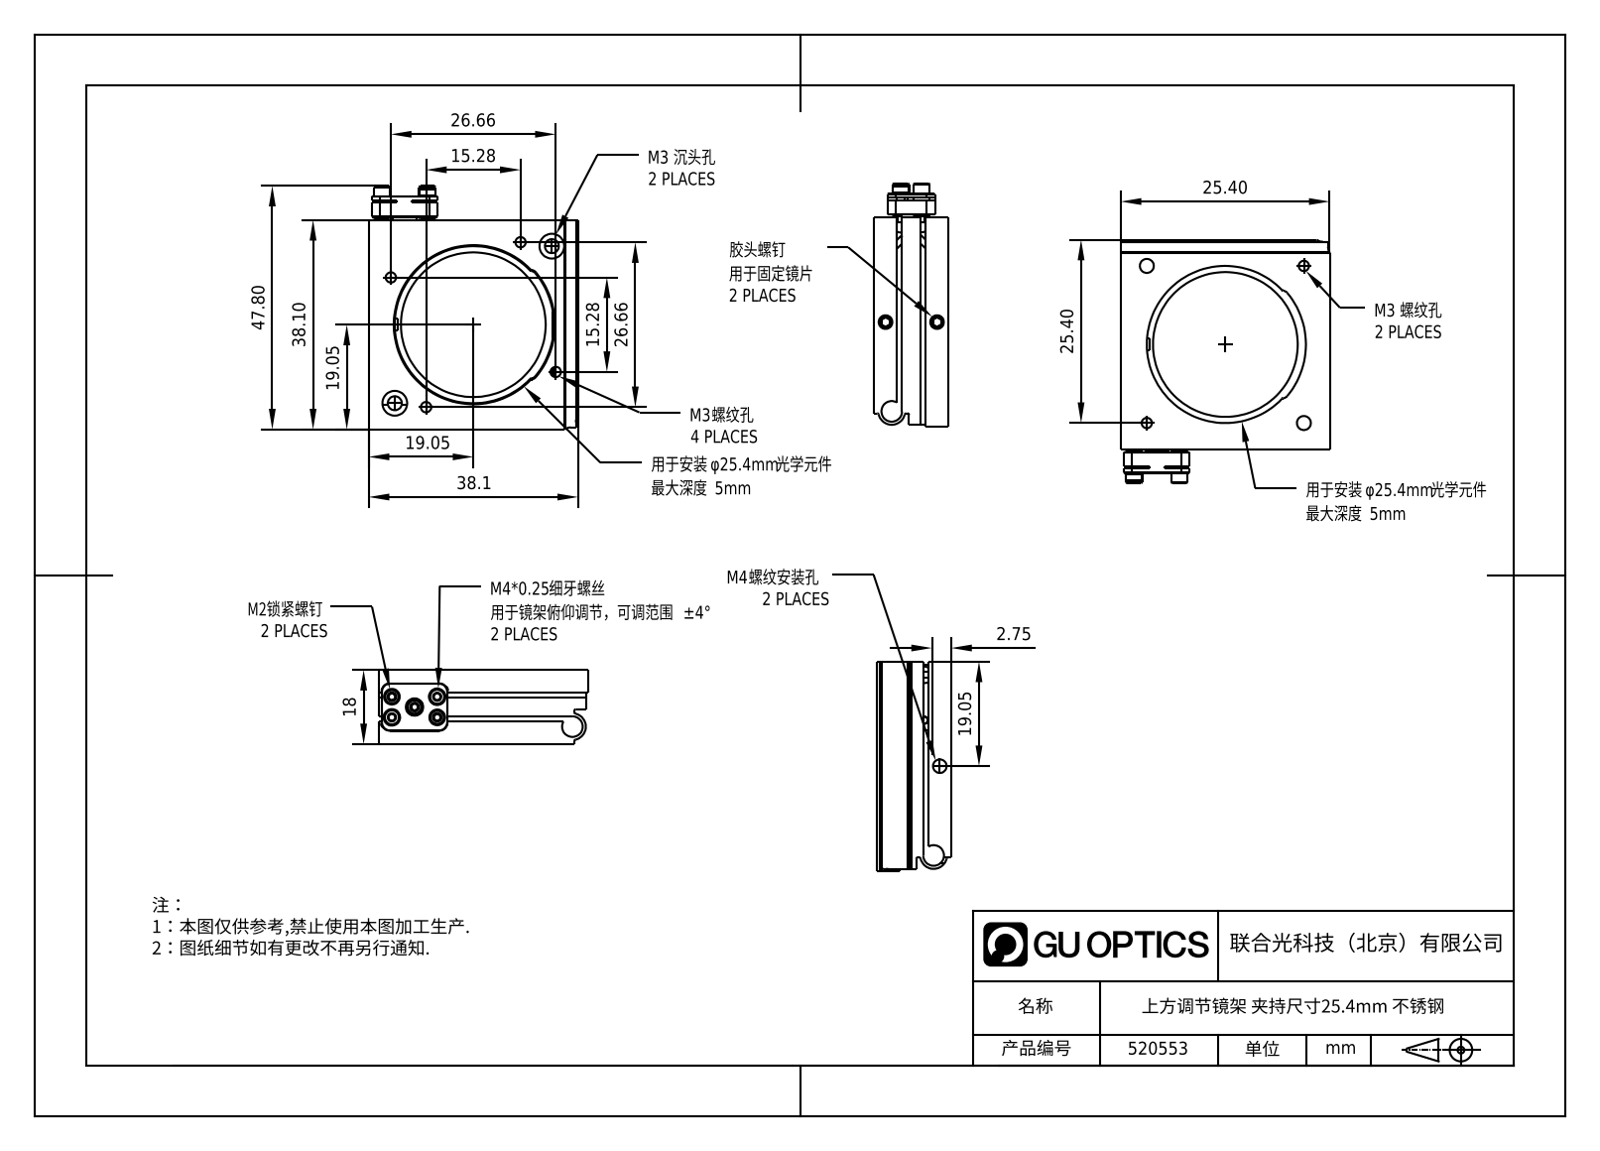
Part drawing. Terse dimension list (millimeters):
name: 1.1.6.22_ZJR-BS1
written by: SolidWorks 2021 (CONFIG_CONTROL_DESIGN)
unit: mm
bodies: 0 solids, 286 faces (100 planar, 118 cylindrical, 68 other)
size: 45.86 × 38.1 × 18
holes: 6× ⌀2.5, 3× ⌀3.3, 2× ⌀1.5, 2× ⌀3.4, 2× ⌀5, 2× ⌀6, 1× ⌀4, 1× ⌀22.4, 1× ⌀25.4
bosses: 4× ⌀1.5, 2× ⌀4, 2× ⌀3.8, 1× ⌀3
rounds: 6× R0.35, 5× R2, 4× R1.5, 2× R0.5, 2× R2.25, 2× R2.5, 2× R3.25, 1× R0.75
face distances: 5.75, 6.75, 11.25, 1.25, 5.5, 12.5, 4.5, 7, 18, 0.5
hole spacings: 5.1, 15.36, 17.96, 20.35, 21.73, 25.4, 26.52, 33.03
